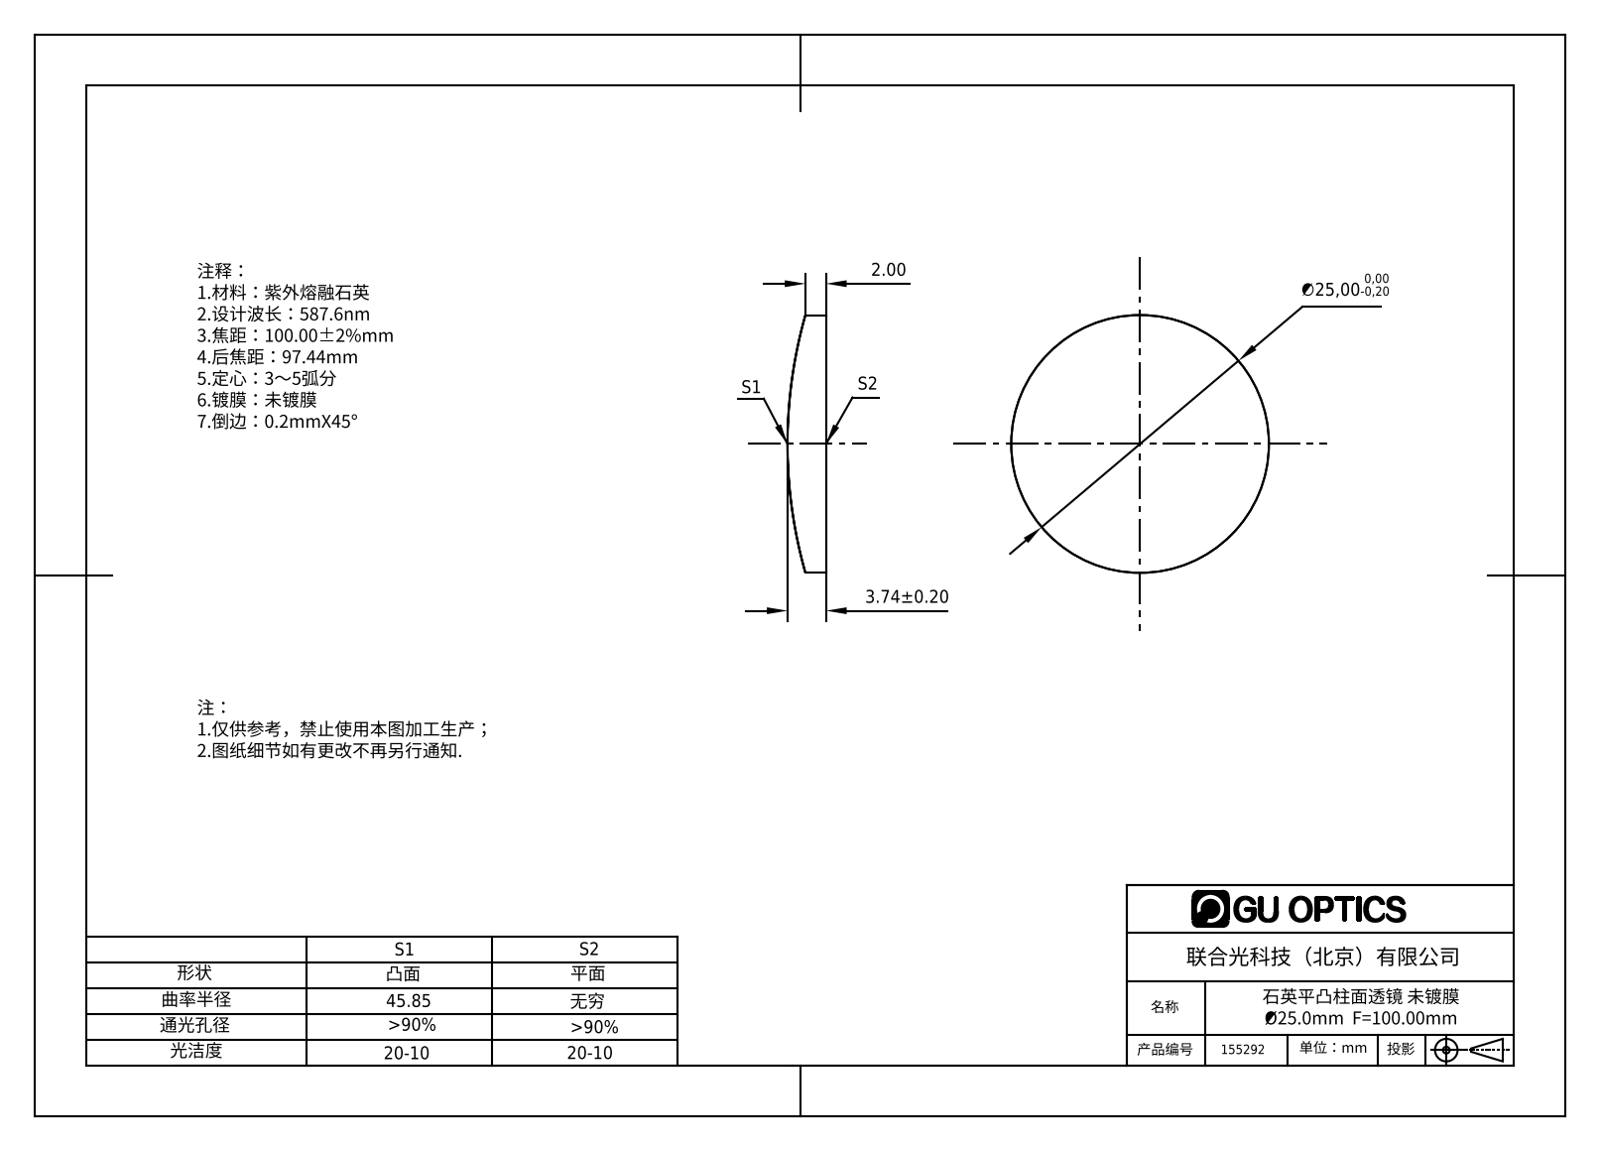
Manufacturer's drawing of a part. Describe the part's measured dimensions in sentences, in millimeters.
The part is named "155292". Its 3-D file was written by "SolidWorks 2016 (AUTOMOTIVE_DESIGN)". It is 1 solid with 4 faces: 1 planar, 3 cylindrical and 0 other. Overall it measures 25 by 25 by 3.74 millimeters. Its volume is 1 625 cubic millimeters and its surface area 1 212 square millimeters. Round bosses or shafts: 1 of diameter 25. Partial cylindrical surfaces (rounded edges, fillets, slot ends): 1 of radius 45.85.
